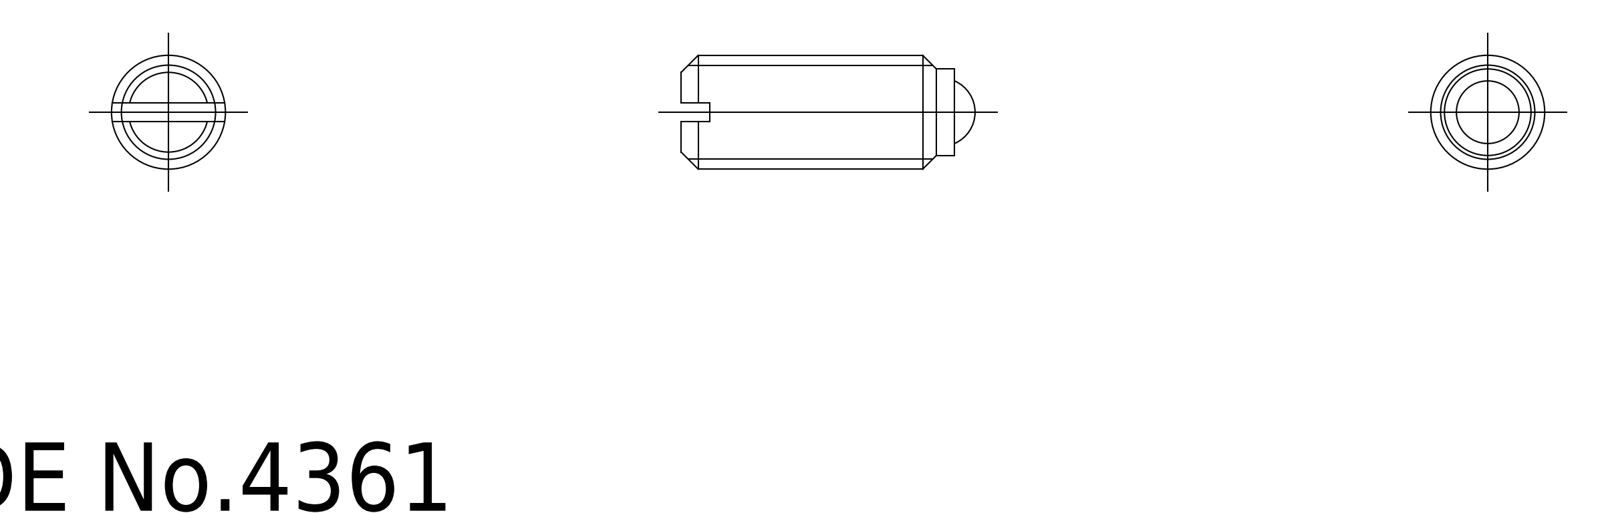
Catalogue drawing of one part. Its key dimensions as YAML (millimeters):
part_name: "ball; PBF_5_14567_36"
step_written_by: "CADfix (AUTOMOTIVE_DESIGN)"
units: millimeters
bodies: {solids: 2, faces: 19, planar: 0, cylindrical: 0, other: 19}
overall_size: [12.9, 5, 5]
volume: 207
surface_area: 283
